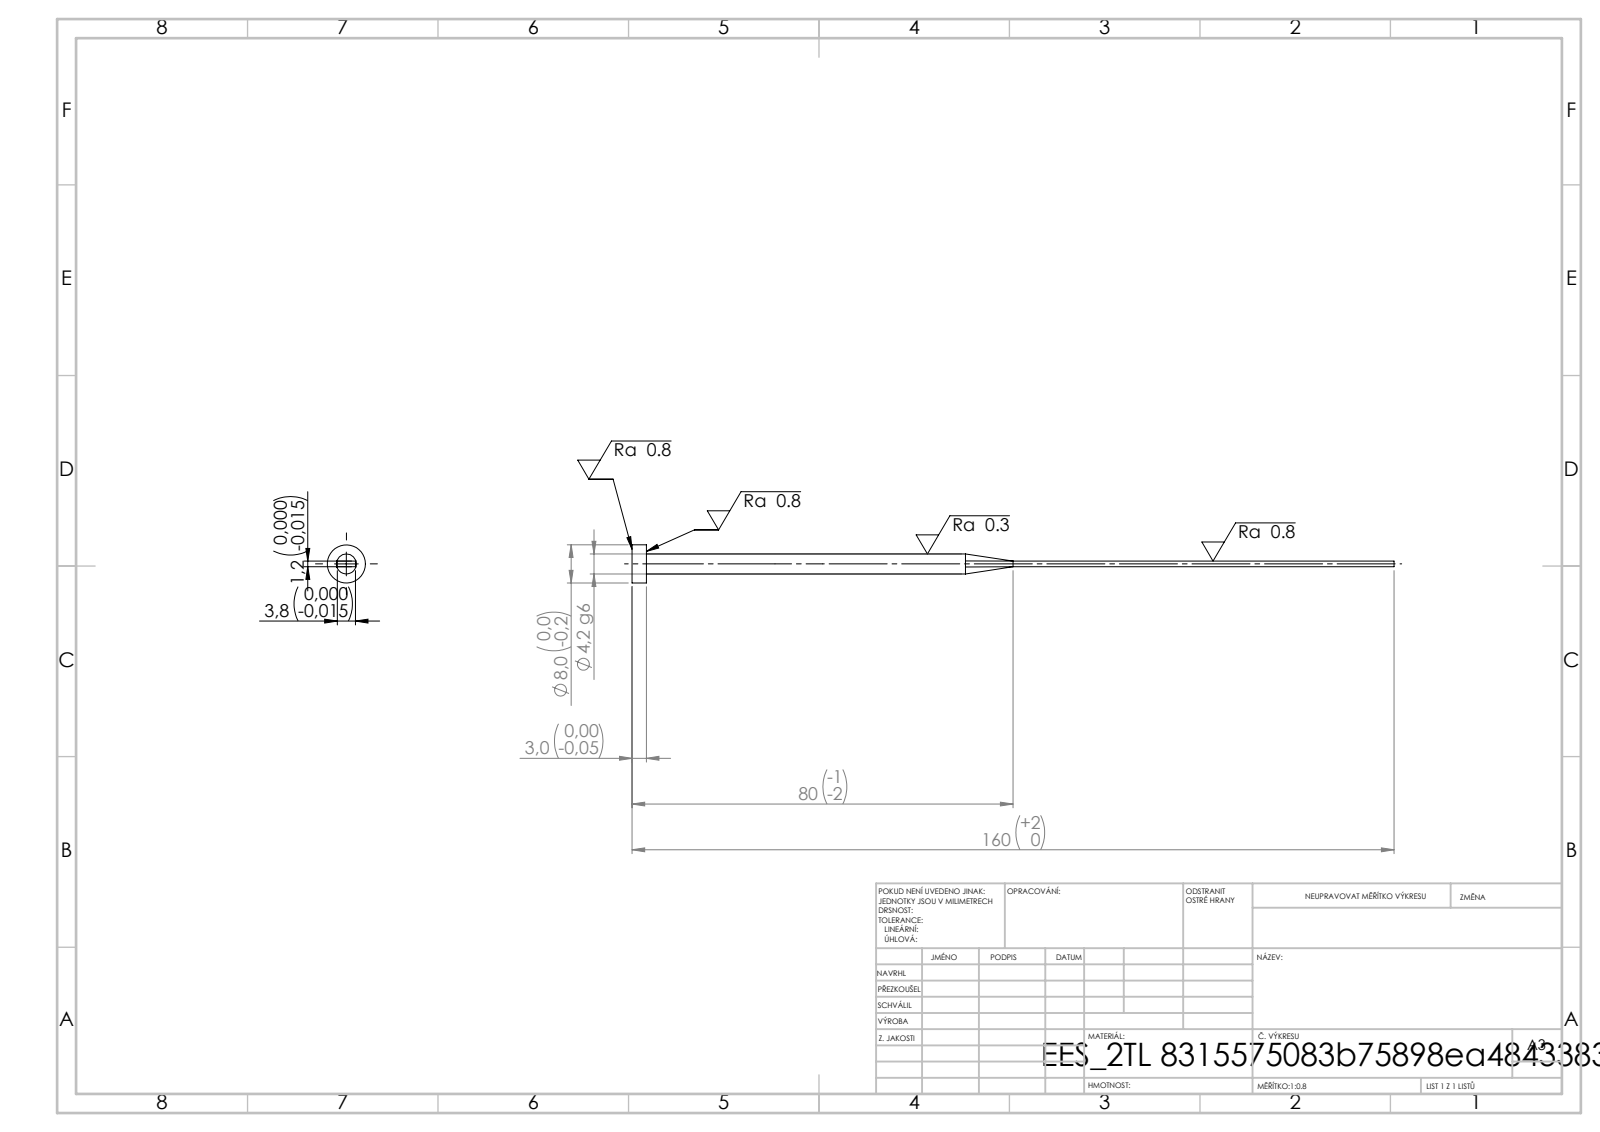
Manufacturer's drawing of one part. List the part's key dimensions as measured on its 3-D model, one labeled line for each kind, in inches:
STEP written by: SolidWorks 2019 (CONFIG_CONTROL_DESIGN)
Units: inches
Bodies: 1 solid, 15 faces (7 planar, 4 cylindrical, 4 other)
Overall size (bounding box): 6.299 × 0.315 × 0.315
Volume: 0.094 in³ · Surface area: 3.043 in²
Round bosses / shafts (diameter × count): ⌀0.315 ×1, ⌀0.165 ×1
Main face-to-face distances: 0.047, 0.15, 0.118, 6.299, 6.181
